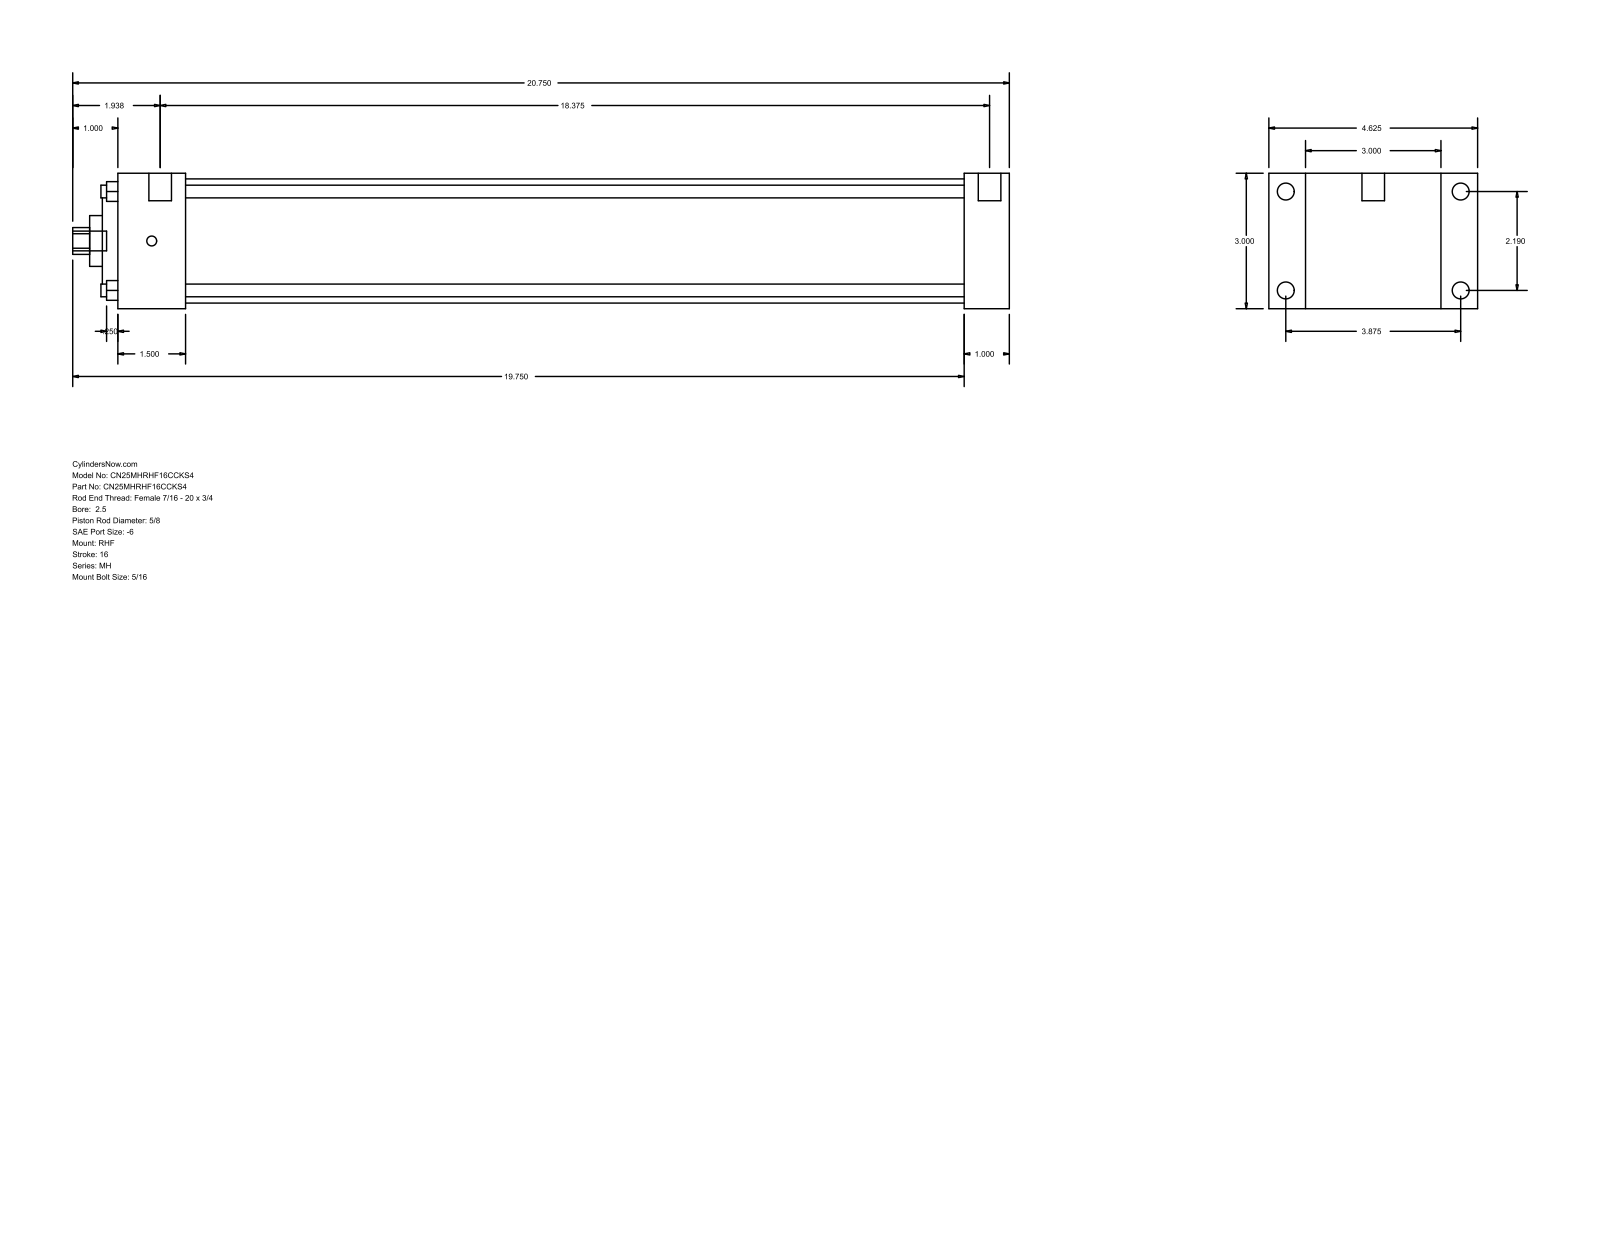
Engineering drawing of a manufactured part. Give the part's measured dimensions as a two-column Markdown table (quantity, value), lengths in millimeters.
| quantity | value |
| --- | --- |
| part name | MH_RHF__0250_0.625 |
| STEP written by | GSSL Pune (CONFIG_CONTROL_DESIGN) |
| units | millimeters |
| bodies | 0 solids, 90 faces (61 planar, 29 cylindrical, 0 other) |
| overall size | 527.05 × 117.47 × 76.2 |
| round holes (diameter × count) | 7.14 × 4, 15.88 × 1, 28.57 × 1, 55.55 × 1, 69.85 × 1 |
| round bosses / shafts (diameter × count) | 9.53 × 4, 5.56 × 4, 12.7 × 2, 11.11 × 1 |
| partial cylindrical surfaces (radius × count) | 7.54 × 1 |
| main face-to-face distances | 76.2, 25.4, 20.64, 96.84, 501.65, 476.25, 117.48, 38.1, 438.15, 463.55 |
| hole center spacings | 39.33, 55.62, 78.66 |
